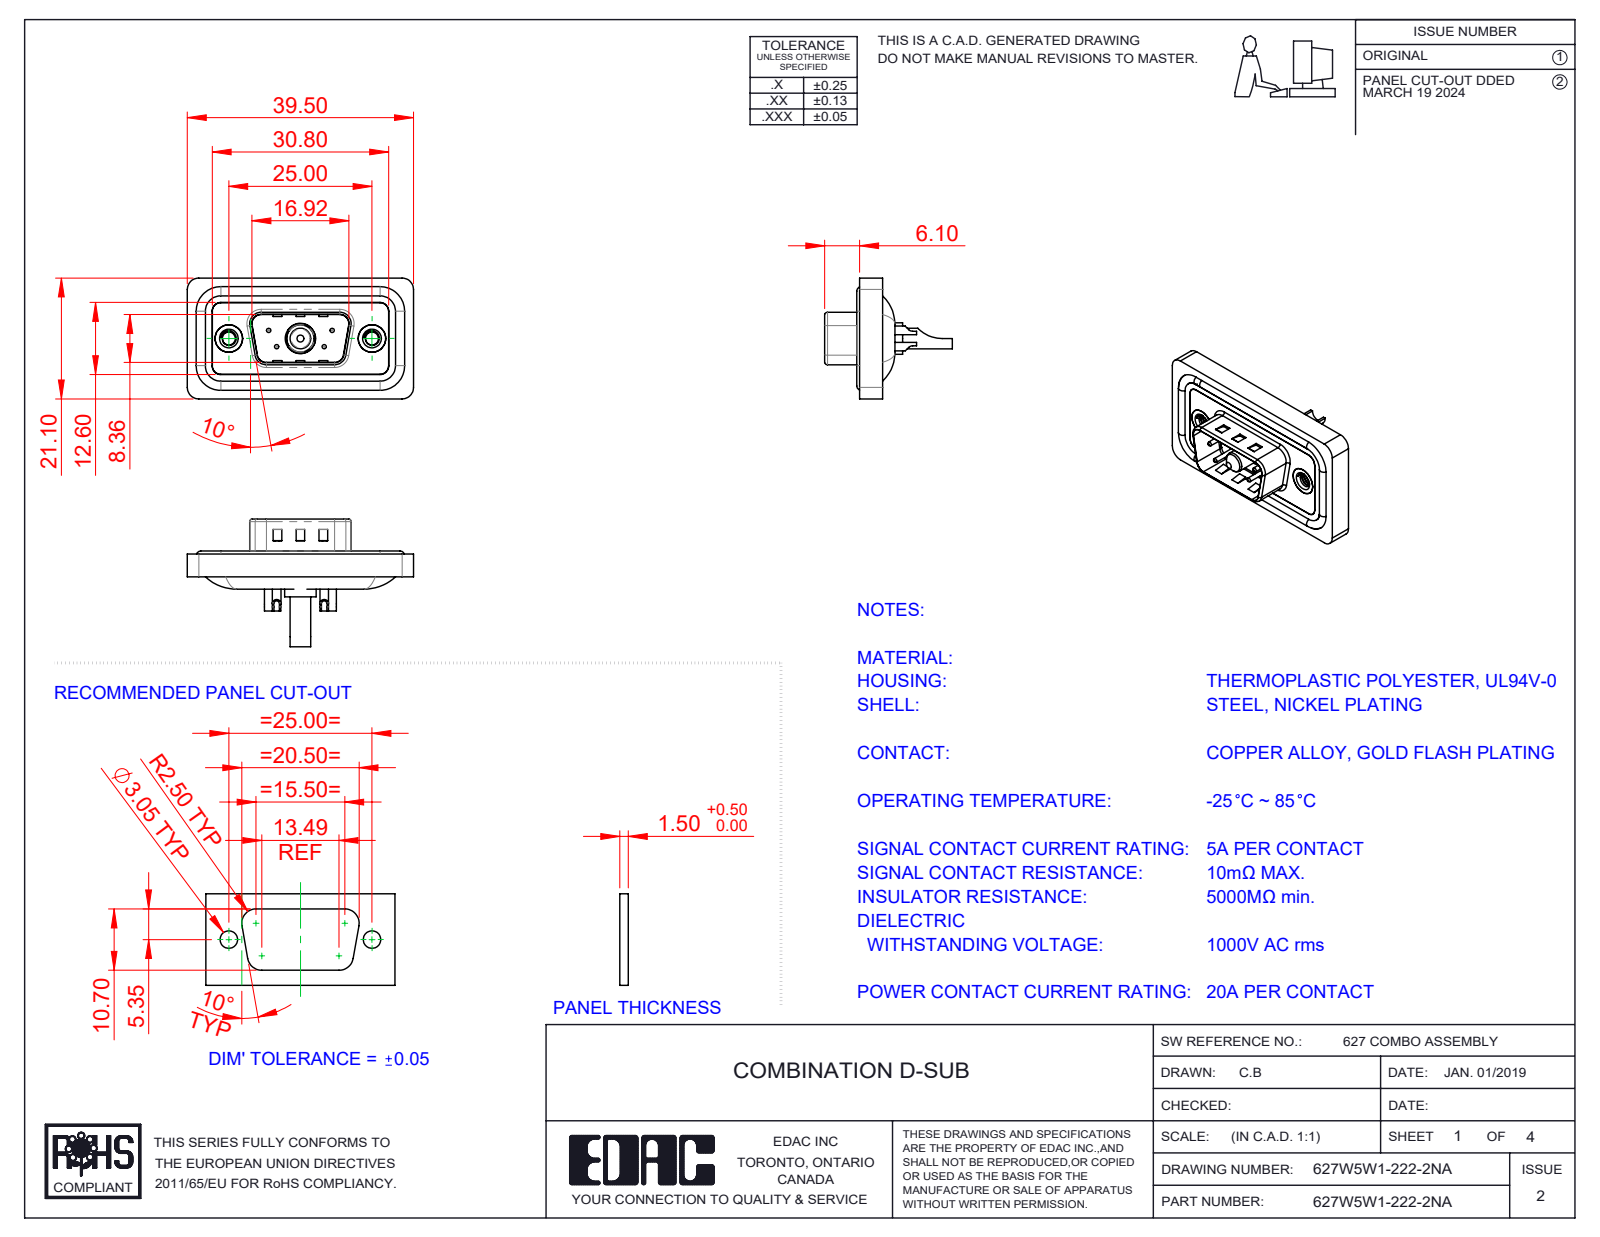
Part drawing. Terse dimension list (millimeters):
name: 627Combo Shell Rear_09 Contacts; 627Combo Waterproof Housing_09 Contacts; 627Combo Threaded Rivet_A; 627Combo Contact Row 2_22 (+5 more)
written by: SolidWorks 2023 (CONFIG_CONTROL_DESIGN)
unit: mm
bodies: 13 solids, 603 faces (194 planar, 268 cylindrical, 141 other)
size: 39.5 × 22.3 × 21.1
volume: 4 408 mm³; area: 7 053 mm²
holes: 4× ⌀0.75, 4× ⌀1, 4× ⌀1.6, 4× ⌀2, 2× ⌀2.26, 2× ⌀4, 2× ⌀4.8, 2× ⌀5, 1× ⌀2.7, 1× ⌀4.85, 1× ⌀5.3
bosses: 4× ⌀1.6, 4× ⌀1.5, 2× ⌀4.9, 1× ⌀5.5, 1× ⌀5.2, 1× ⌀4.75, 1× ⌀3.75, 1× ⌀3.6
rounds: 22× R1.5, 18× R2, 8× R0.5, 8× R1.6, 6× R1, 4× R0.25, 4× R0.6, 4× R0.65
face distances: 0.4, 1.1, 2.9, 1.6, 3.1, 0.5, 1.5, 2.5, 4, 0.8
hole spacings: 3.16, 5.72, 7.1, 12.5, 18.1, 4.39, 4.4, 8.31
